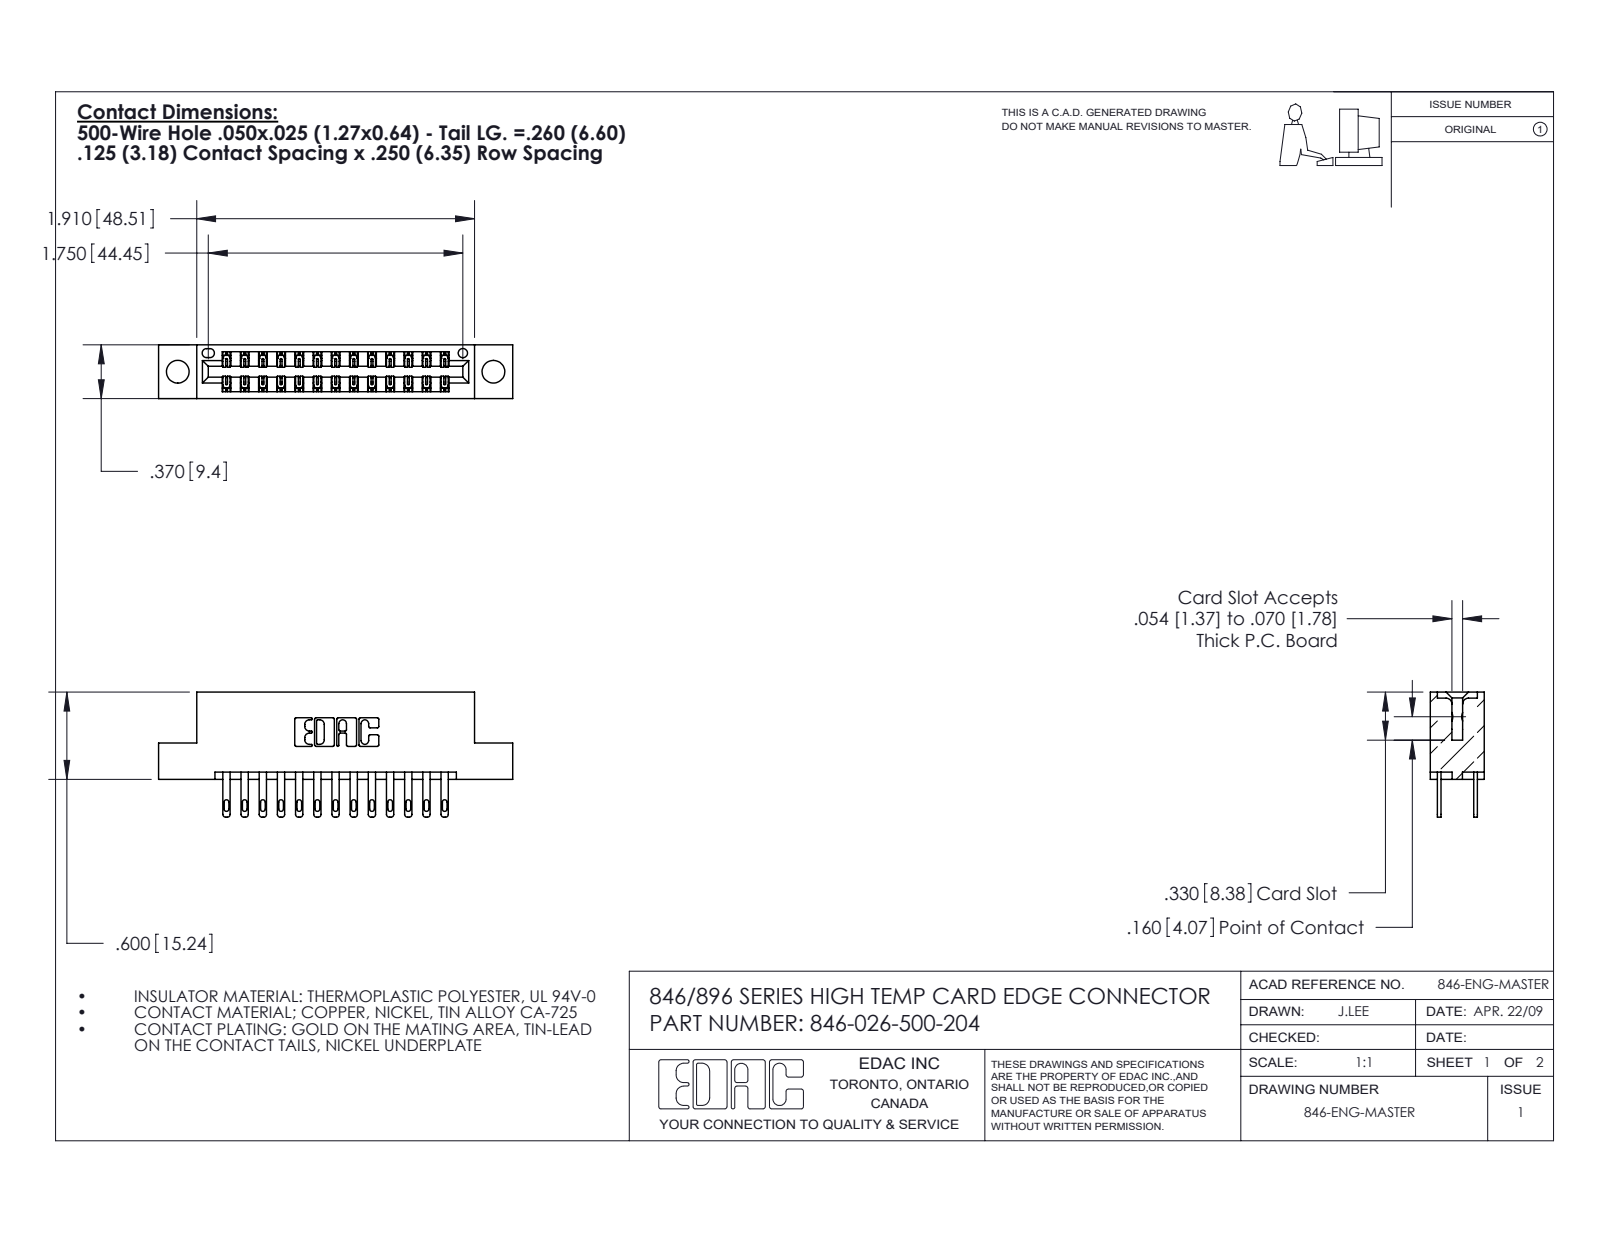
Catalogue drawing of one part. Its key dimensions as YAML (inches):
part_name: "345-292-001_345-293-100; 346-026-500-204; 346 Part_Flush Mounting Lugs - 0.156 Dia-TH"
step_written_by: "SolidWorks 2016 (CONFIG_CONTROL_DESIGN)"
units: inches
bodies: {solids: 27, faces: 1370, planar: 830, cylindrical: 540, other: 0}
overall_size: [2.435, 0.86, 0.37]
volume: 0.354
surface_area: 11.78
round_holes:
  - {diameter: 0.156, count: 2}
  - {diameter: 0.064, count: 1}
partial_cylinders:
  - {radius: 0.006, count: 39}
  - {radius: 0.016, count: 26}
  - {radius: 0.02, count: 26}
  - {radius: 0.01, count: 22}
  - {radius: 0.007, count: 6}
  - {radius: 0.031, count: 6}
  - {radius: 0.026, count: 3}
  - {radius: 0.014, count: 2}
face_to_face_distances: [0.25, 0.048, 0.322, 0.37, 0.072, 0.298, 0.025, 0.275, 0.148, 0.222]
hole_center_spacings: [0.246, 1.964, 2.17]
